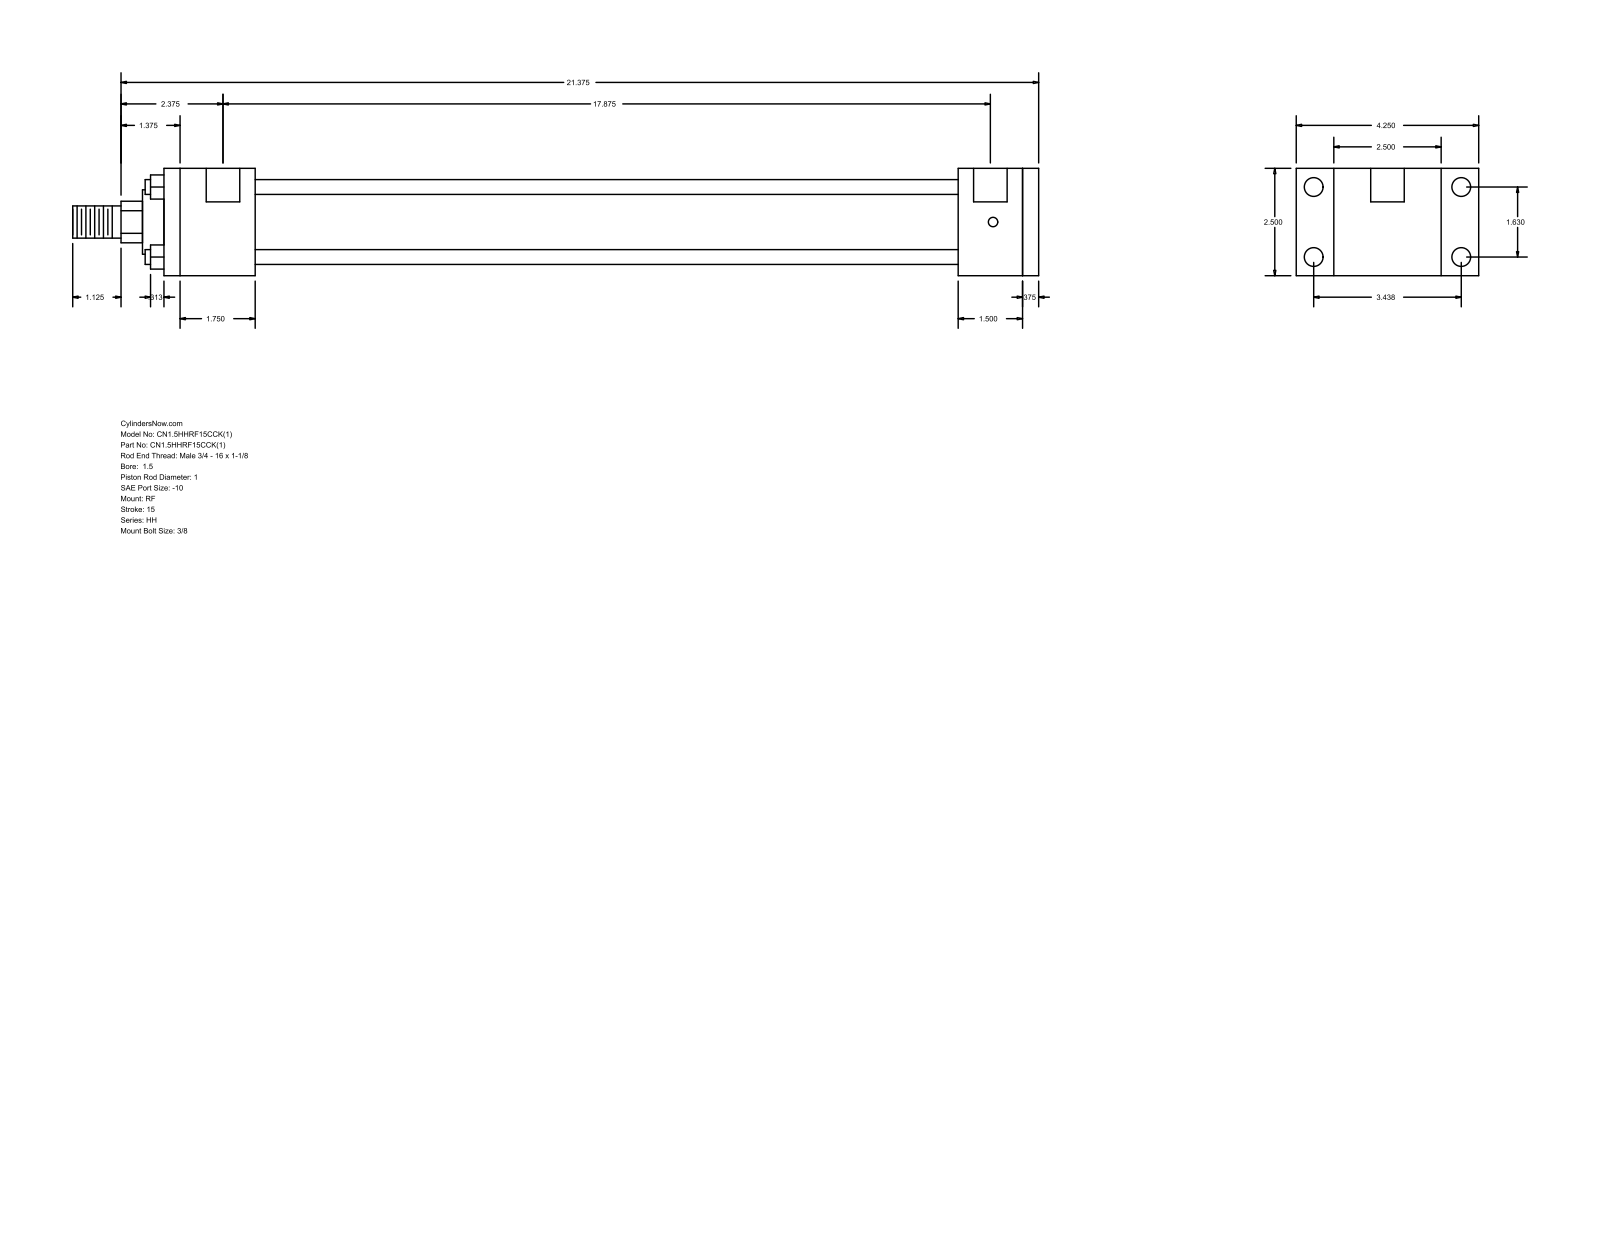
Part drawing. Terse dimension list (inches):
name: HH_RF__0150_1
written by: GSSL Pune (CONFIG_CONTROL_DESIGN)
unit: in
bodies: 0 solids, 92 faces (64 planar, 28 cylindrical, 0 other)
size: 22.5 × 4.25 × 2.5
holes: 4× ⌀0.219, 4× ⌀0.438, 2× ⌀0.781
bosses: 4× ⌀0.345, 1× ⌀1.75, 1× ⌀1.5, 1× ⌀1, 1× ⌀0.75
rounds: 1× R0.484
face distances: 2.5, 0.375, 1.5, 16.375, 17.875, 18.25, 1.875, 2.125, 18.5, 20
hole spacings: 0.063, 1.63, 3.438, 3.805, 17.937, 18, 17.875
